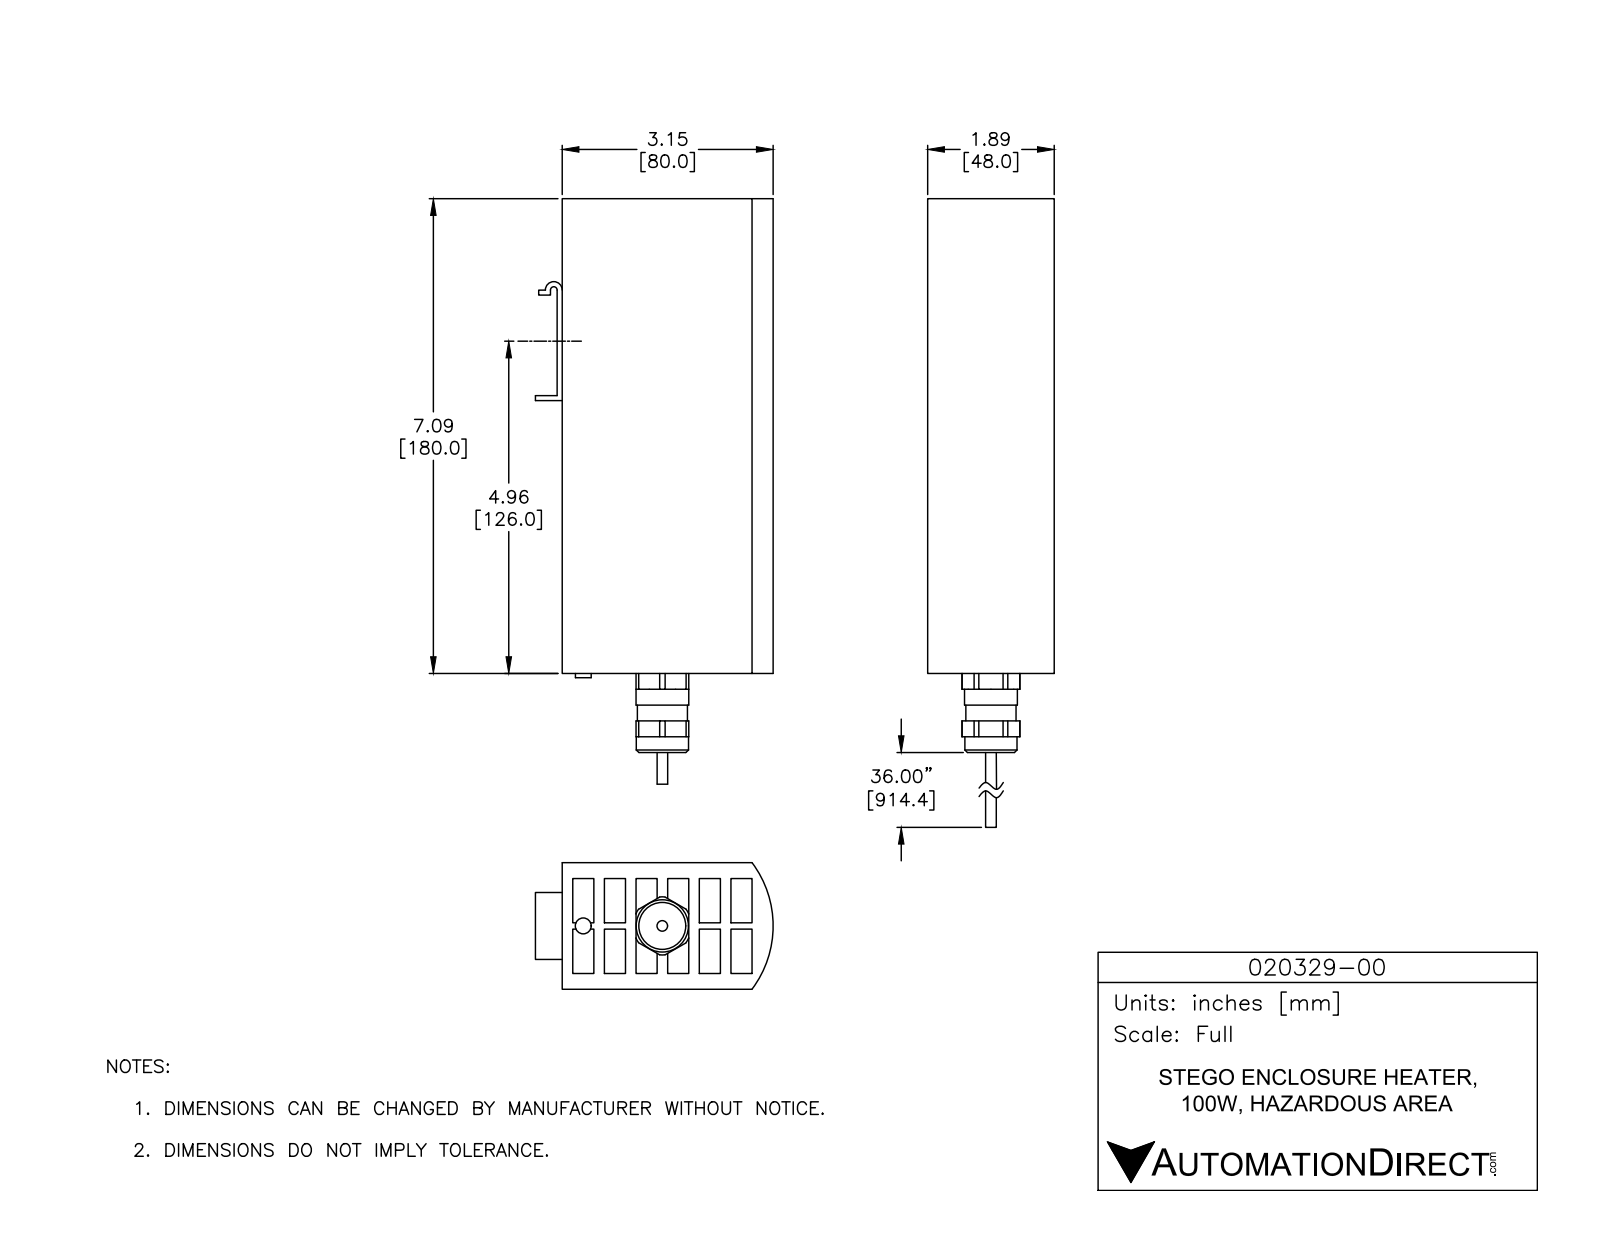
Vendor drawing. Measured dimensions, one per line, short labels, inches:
name: 020320-00
written by: SolidWorks 2017 (AUTOMOTIVE_DESIGN)
unit: in
bodies: 3 solids, 125 faces (109 planar, 14 cylindrical, 2 other)
size: 8.739 × 3.55 × 1.89
volume: 24.52 in³; area: 244.7 in²
bosses: 1× ⌀0.787, 1× ⌀0.748, 1× ⌀0.16
rounds: 1× R0.05, 1× R0.125, 1× R1.575
face distances: 0.472, 0.945, 1.417, 1.89, 0.157, 0.315, 0.787, 0.63, 1.102, 1.26
